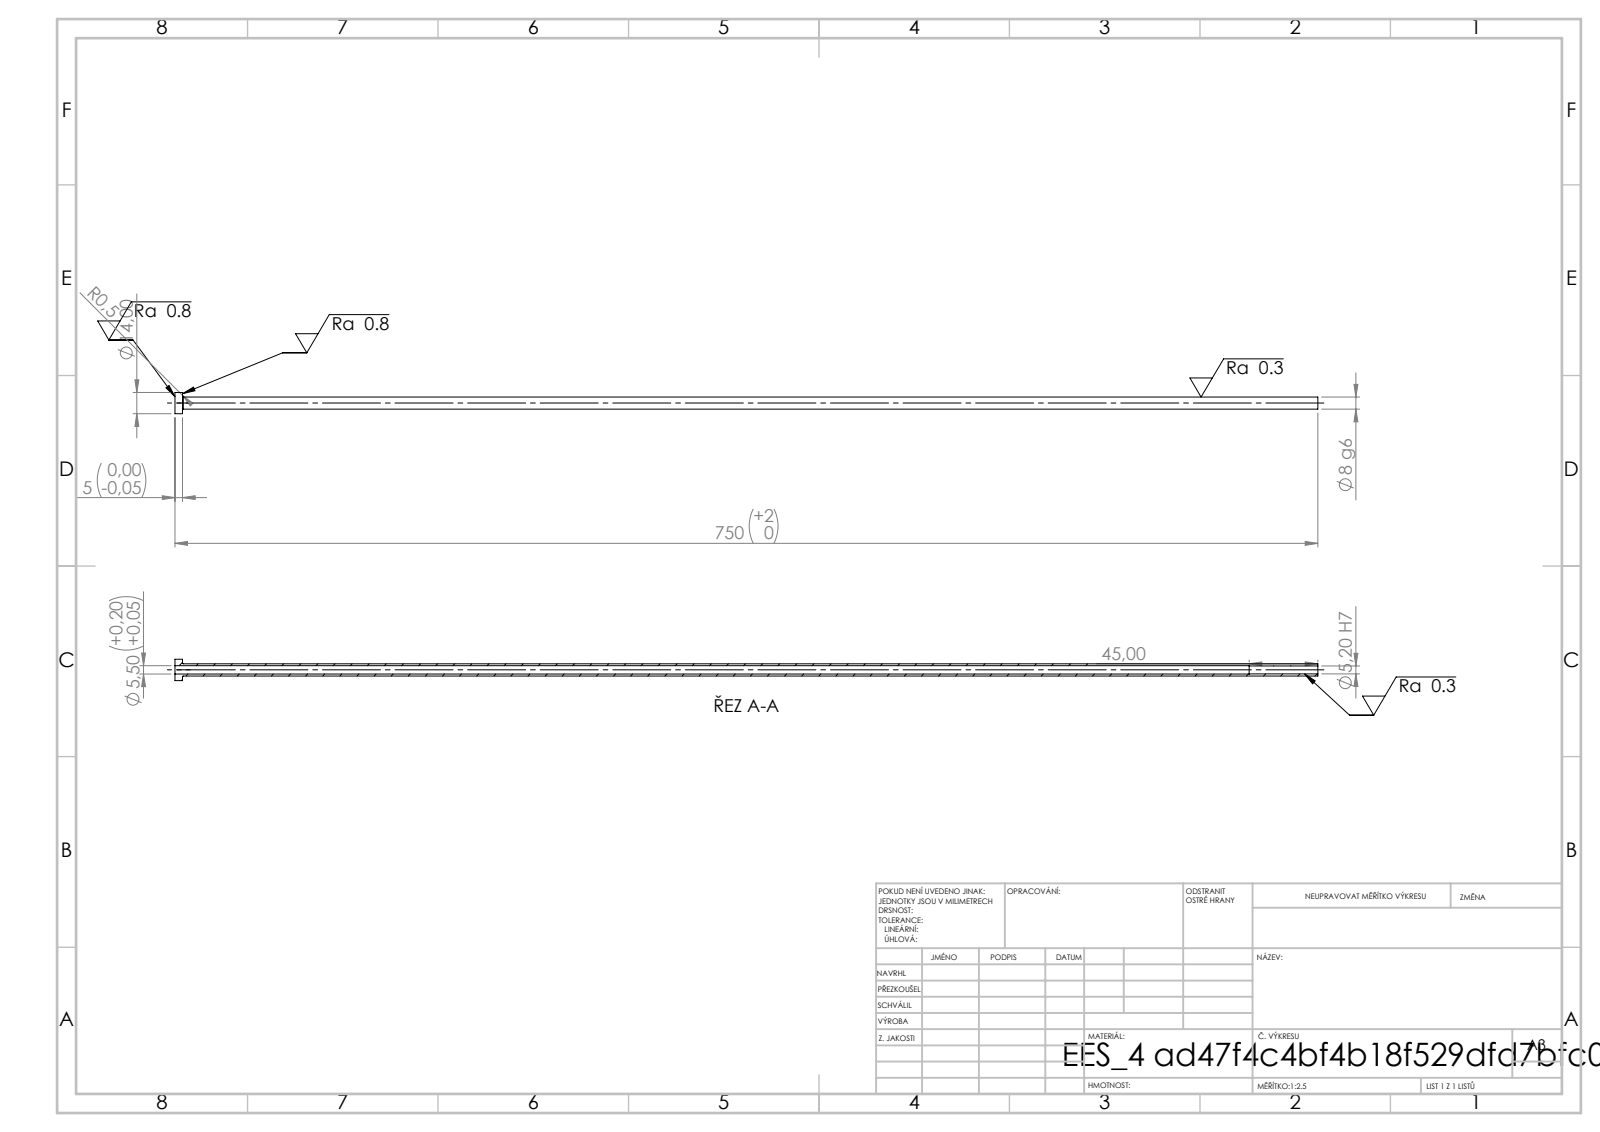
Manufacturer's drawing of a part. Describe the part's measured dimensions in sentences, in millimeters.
Its 3-D file was written by "SolidWorks 2019 (CONFIG_CONTROL_DESIGN)". It is 1 solid with 14 faces: 4 planar, 8 cylindrical and 2 other. Overall it measures 750 by 14 by 14 millimeters. Its volume is 20 514 cubic millimeters and its surface area 32 121 square millimeters. Round holes: 1 of diameter 5.2, 1 of diameter 5.5. Round bosses or shafts: 1 of diameter 14, 1 of diameter 8. The main face-to-face distances are 5, 750, 745, 705, 700, 45.
